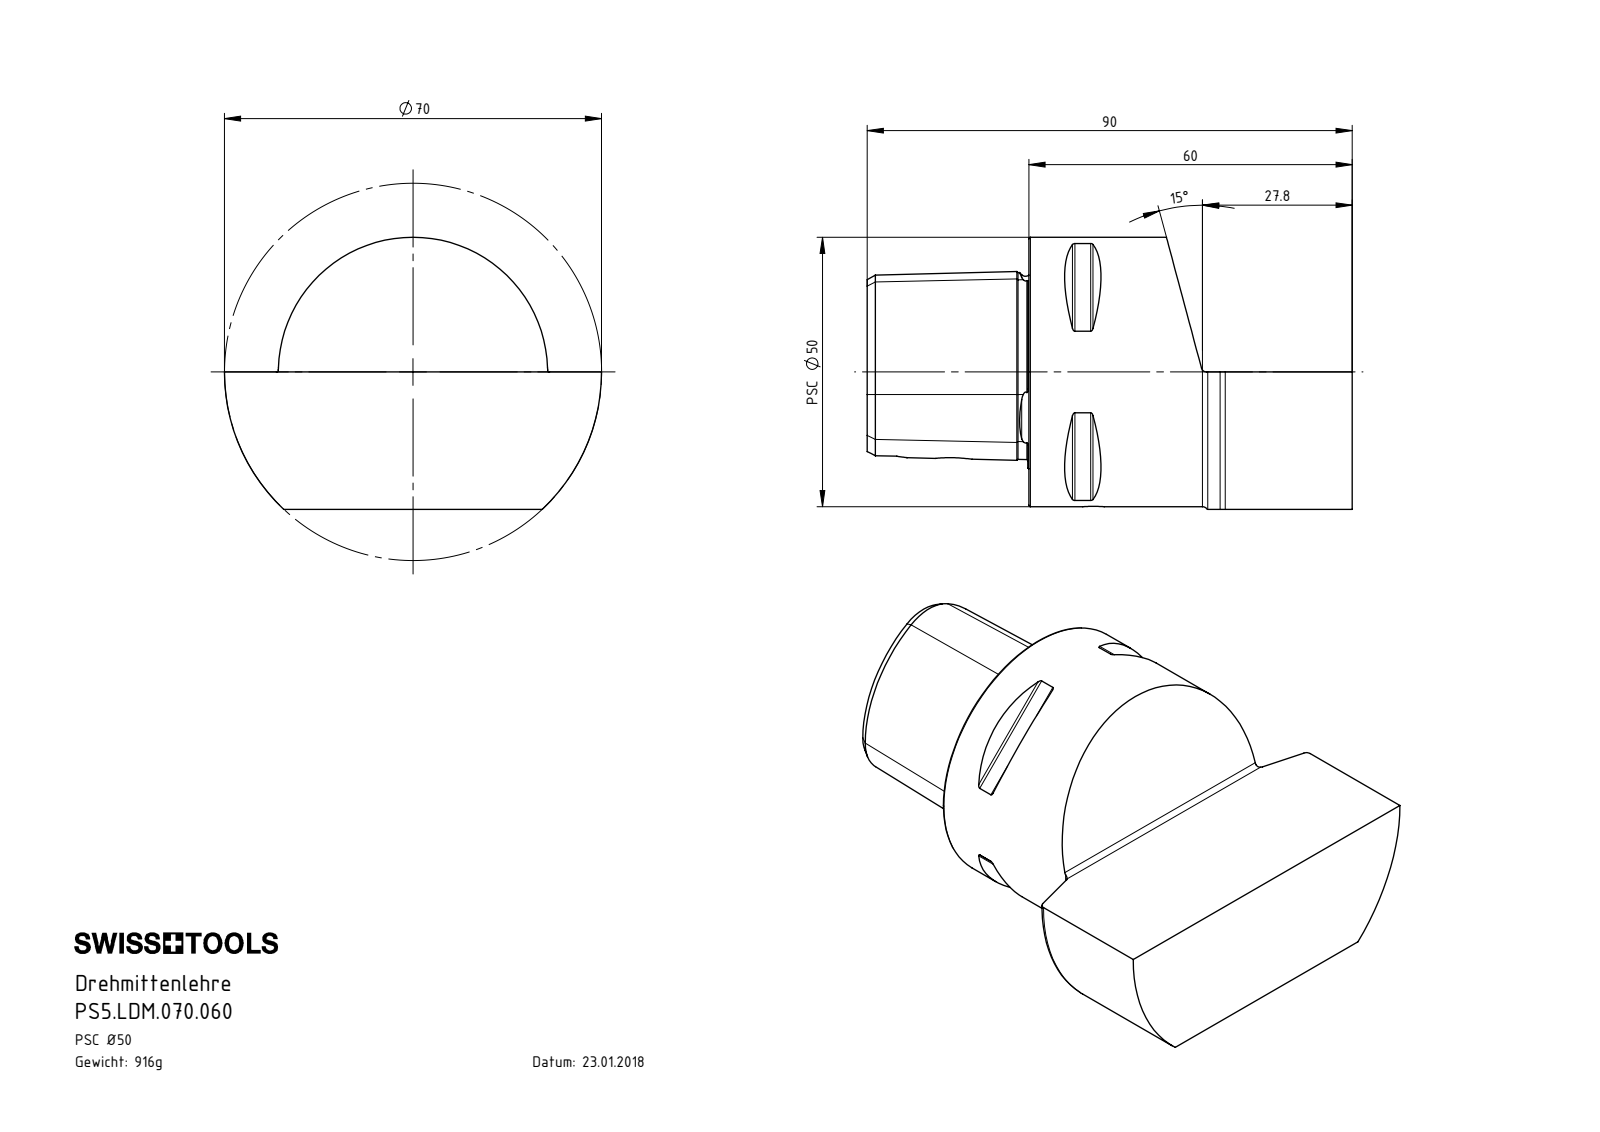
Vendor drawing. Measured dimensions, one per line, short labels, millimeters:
name: PS5-LDM.070.060_A
written by: SolidWorks 2017 (AUTOMOTIVE_DESIGN)
unit: mm
bodies: 1 solid, 128 faces (22 planar, 28 cylindrical, 78 other)
size: 90 × 70 × 50.5
volume: 116 684 mm³; area: 20 891 mm²
holes: 1× ⌀4, 1× ⌀6.1, 1× ⌀14.5, 1× ⌀21, 1× ⌀24
bosses: 1× ⌀50
rounds: 8× R0.5, 1× R1, 1× R4, 1× R35
face distances: 25.5, 60, 30, 90, 19.18, 44.4, 20, 10, 70, 29.8
hole spacings: 26
